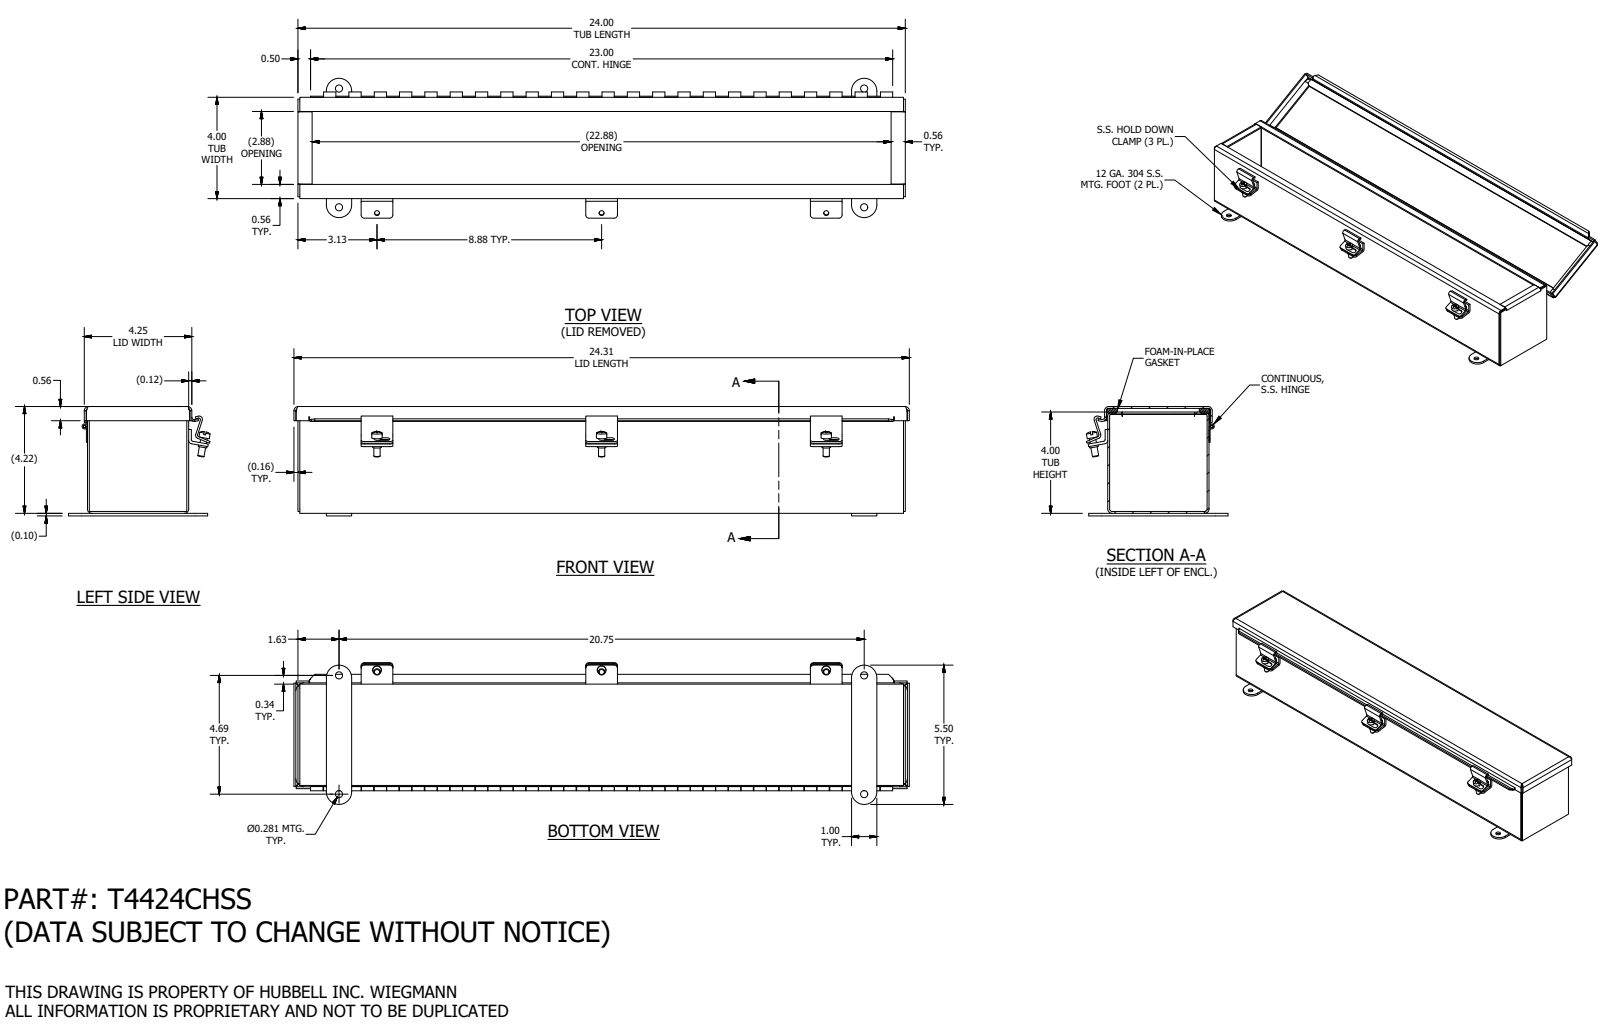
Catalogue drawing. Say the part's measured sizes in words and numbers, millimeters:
The part is named "T4424CHSS". Its 3-D file was written by "SolidWorks 2019 (AUTOMOTIVE_DESIGN)". It is 19 solids with 591 faces: 355 planar, 197 cylindrical and 39 other. Overall it measures 617.6 by 142.2 by 109.8 millimeters. Its volume is 706 600 cubic millimeters and its surface area 738 100 square millimeters. Round holes: 6 of diameter 2.8, 4 of diameter 7.1, 3 of diameter 5, 1 of diameter 2.9. Round bosses or shafts: 3 of diameter 10.4, 3 of diameter 8.7, 3 of diameter 6.4, 1 of diameter 5.1, 1 of diameter 2.5. Partial cylindrical surfaces (rounded edges, fillets, slot ends): 12 of radius 3.2, 11 of radius 2.4, 11 of radius 4.3, 8 of radius 2.2, 6 of radius 3.4, 4 of radius 6.1, 4 of radius 12.7, 3 of radius 1.6. The main face-to-face distances are 1.9, 99.7, 105.3, 101.6, 97.8, 107.1, 103.4, 5.5, 102.9, 3.2. The hole center spacings are 225.4, 19.1, 119, 225.4, 450.9, 527.1, 540.3, 206.4.
